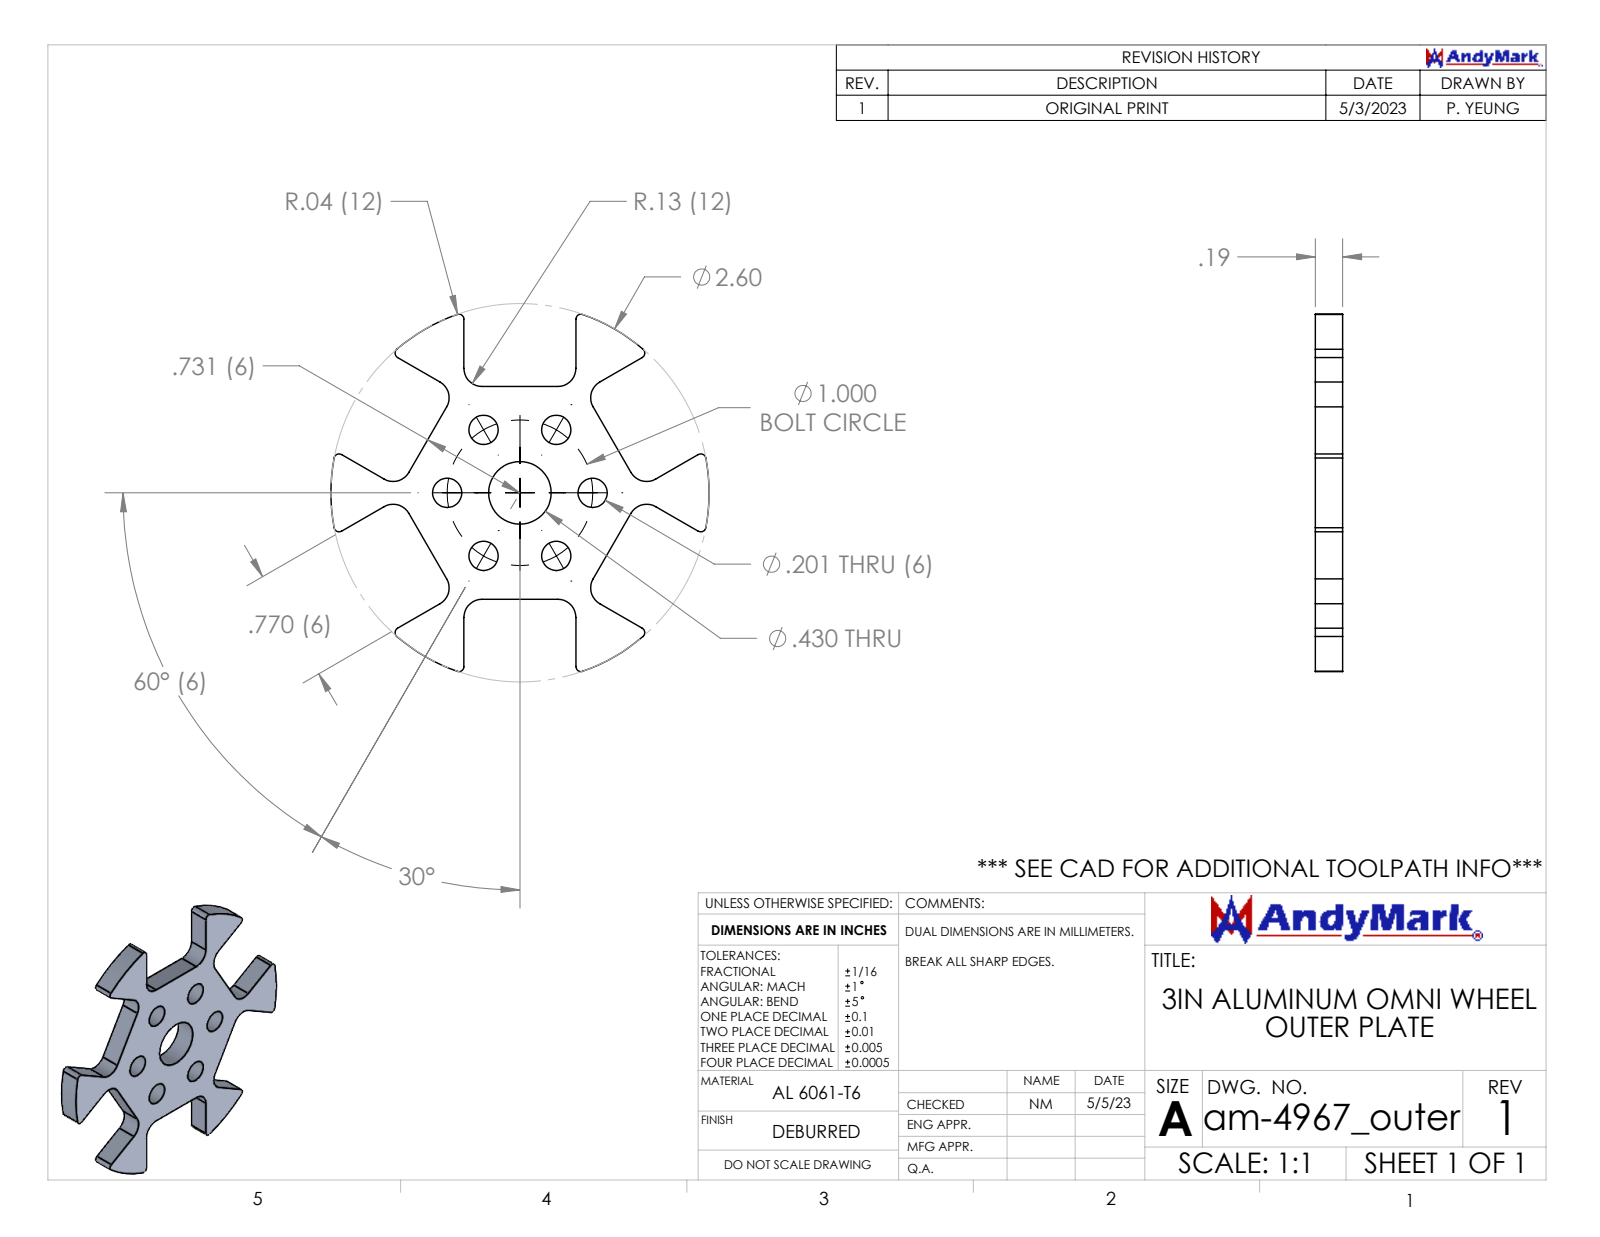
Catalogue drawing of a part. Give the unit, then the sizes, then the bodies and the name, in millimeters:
Units: millimetres
Overall size (bounding box): 66 × 62.4 × 4.8
Round holes (diameter × count): ⌀5.1 ×6, ⌀10.9 ×1
Partial cylindrical surfaces — rounded edges, fillets, slot ends (radius × count): R0.9 ×12, R3.2 ×12, R33 ×1
Main face-to-face distances: 4.7, 19.6, 37.1
Hole centre spacings: 12.7, 22, 25.4
Volume: 7 590 mm³ · Surface area: 5 405 mm²
Bodies: 1 solid, 70 faces (20 planar, 50 cylindrical, 0 other)
Part name (STEP PRODUCT): am-4967_outer 3IN Aluminum Omni Wheel Outer Plate
STEP written by: SolidWorks 2022 (CONFIG_CONTROL_DESIGN)
